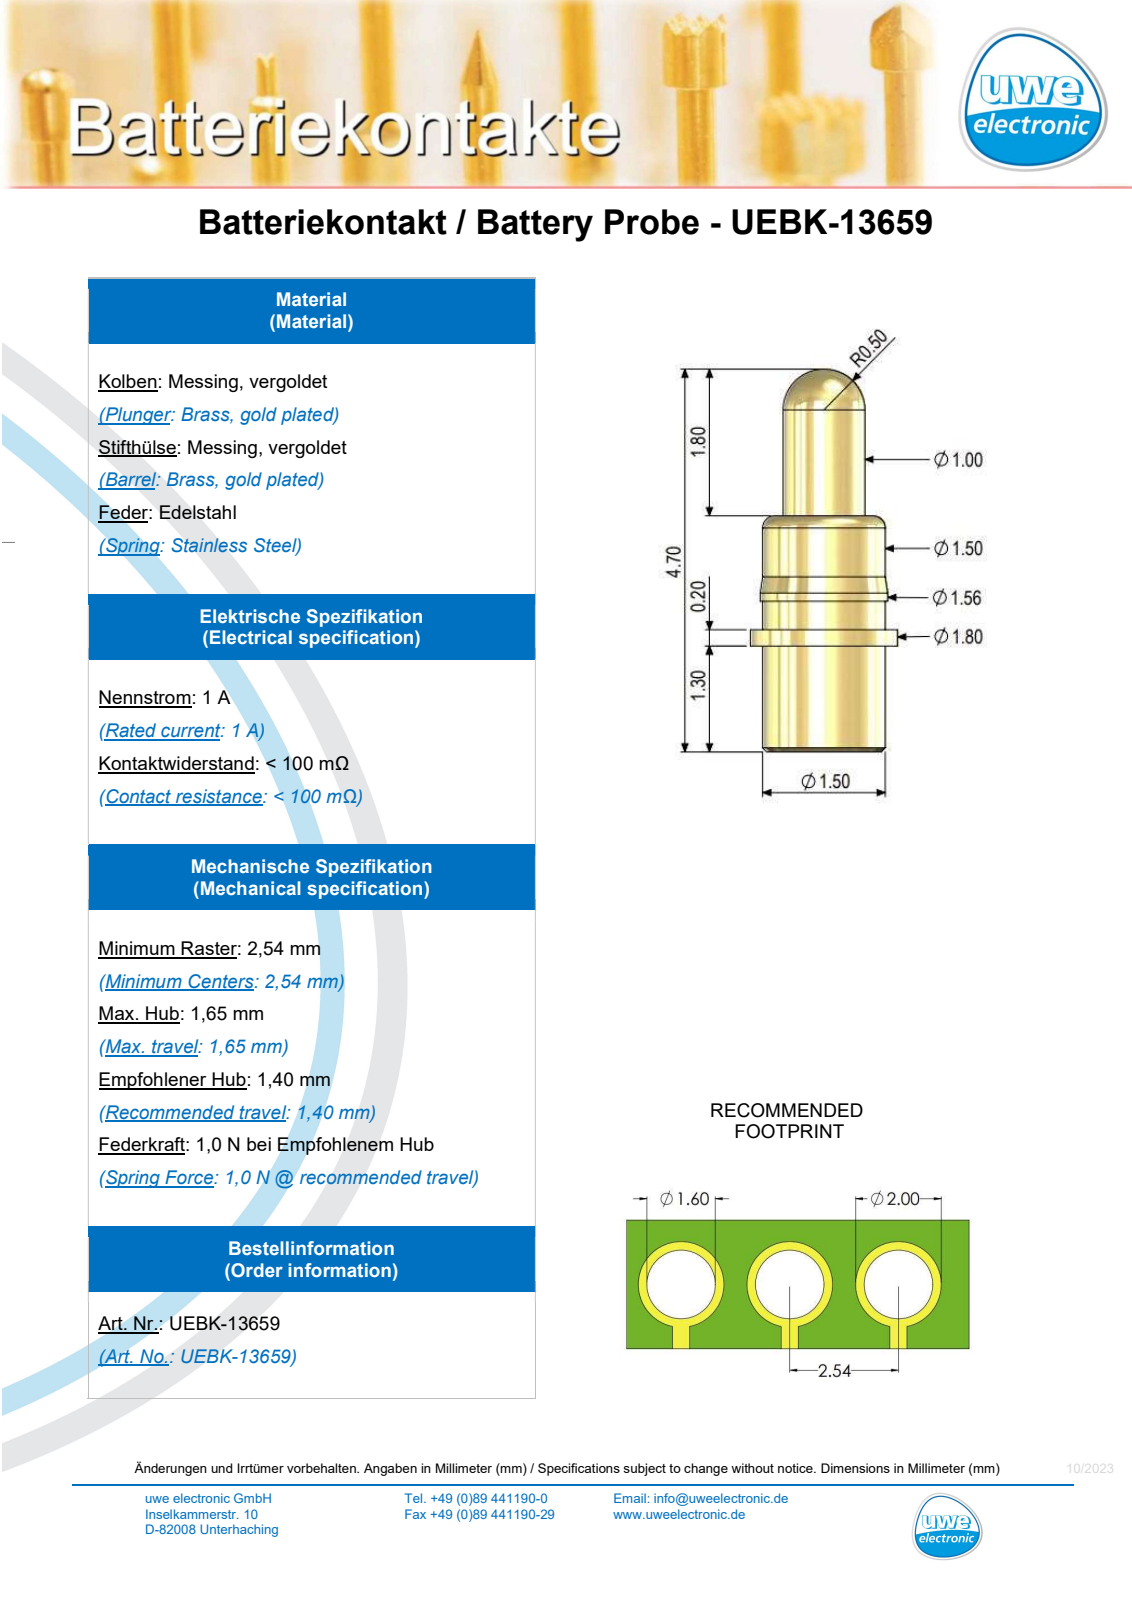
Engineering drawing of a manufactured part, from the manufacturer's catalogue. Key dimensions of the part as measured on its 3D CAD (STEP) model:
Part name (STEP PRODUCT): UEBK-13659_step
STEP written by: SolidWorks 2022 (AUTOMOTIVE_DESIGN)
Units: millimetres
Bodies: 1 solid, 24 faces (5 planar, 12 cylindrical, 7 other)
Overall size (bounding box): 4.7 × 1.8 × 1.8
Volume: 7 mm³ · Surface area: 24 mm²
Round bosses / shafts (diameter × count): ⌀1.8 ×1, ⌀1.56 ×1, ⌀1.5 ×1, ⌀1 ×1
Main face-to-face distances: 1.3, 1.5, 1.4, 1.6, 2.9, 1.05, 0.35, 0.55, 1.85
